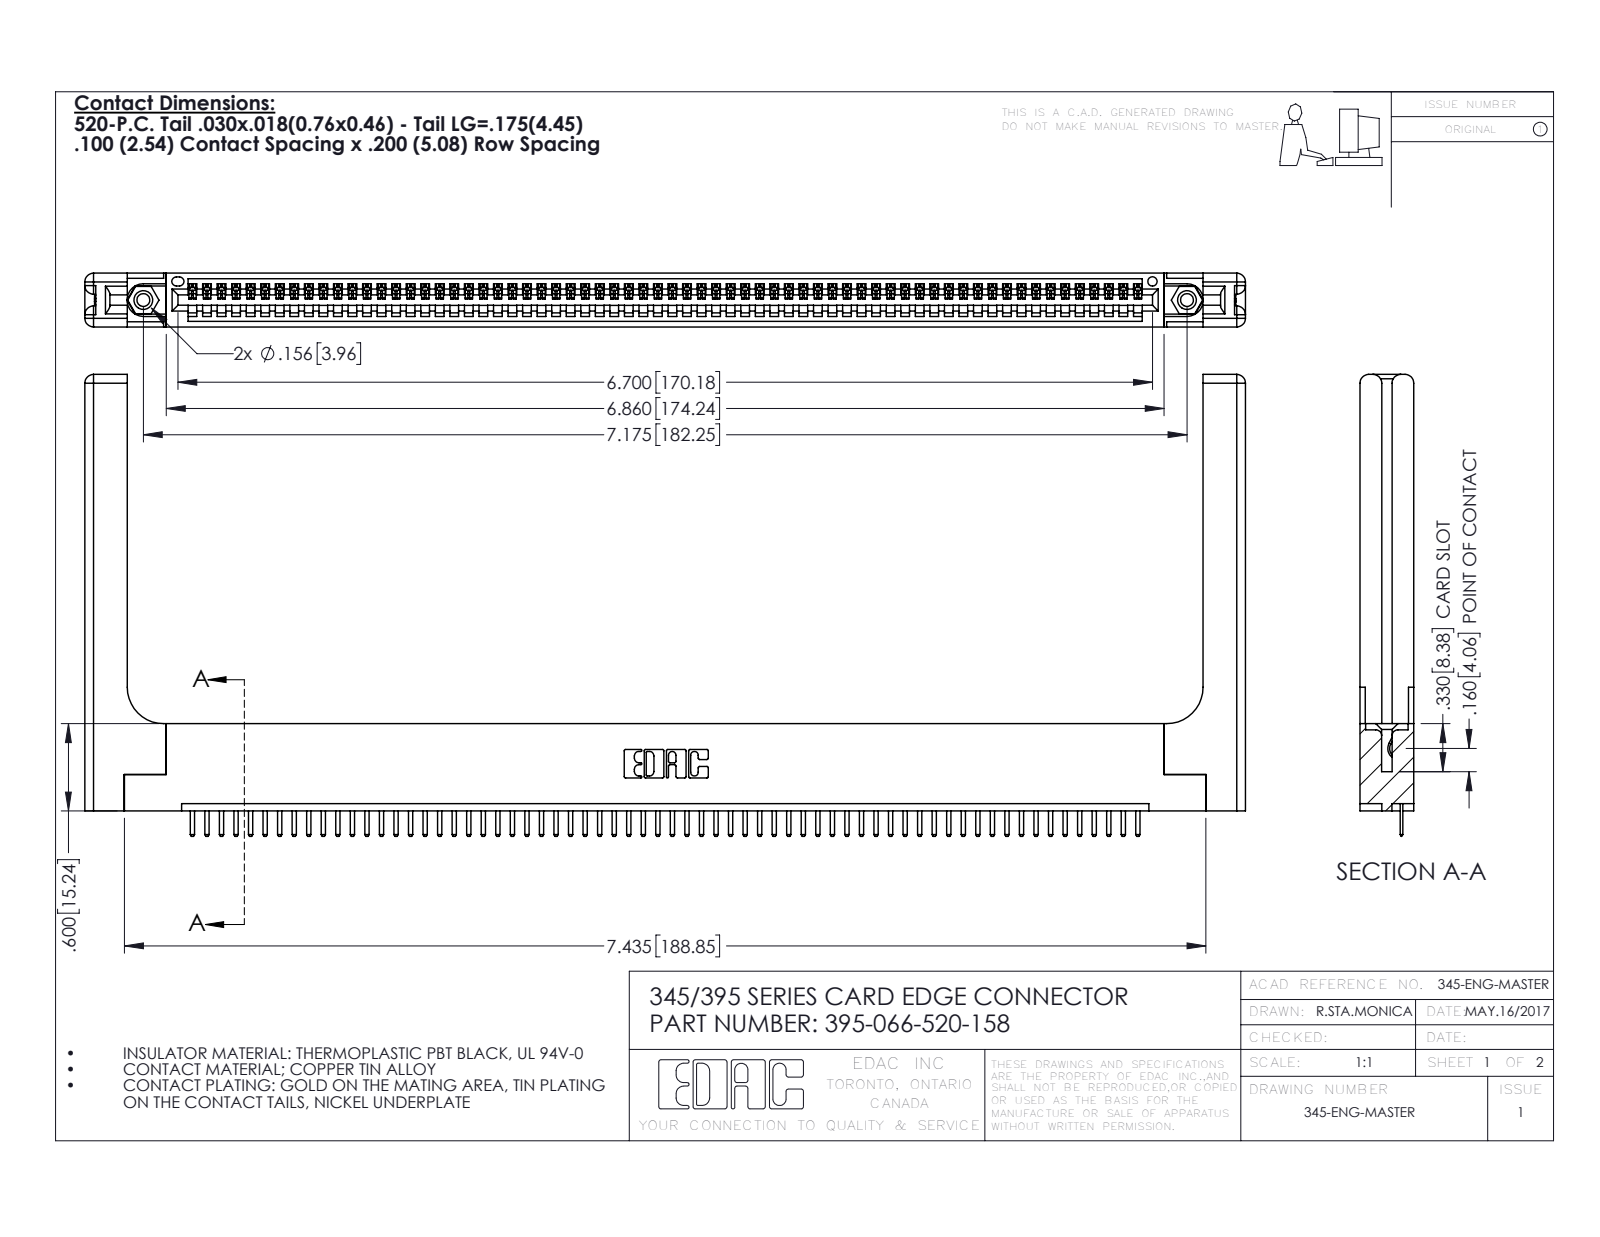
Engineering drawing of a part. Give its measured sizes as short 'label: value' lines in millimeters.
name: 395-066-520-158; 345-292-001_345-293-120; 345-220-058_345-220-058; 345 Part_Flush Mounting Lugs - 0.156 Dia-TH (+1 more)
written by: SolidWorks 2016 (CONFIG_CONTROL_DESIGN)
unit: mm
bodies: 71 solids, 4474 faces (3000 planar, 1414 cylindrical, 60 other)
size: 202.7 × 80.6 × 9.4
volume: 27 760 mm³; area: 30 600 mm²
holes: 2× ⌀2.3, 2× ⌀3.2, 2× ⌀4, 1× ⌀1.6
bosses: 2× ⌀3.9
rounds: 134× R0.3, 132× R0.2, 22× R0.3, 16× R1.5, 6× R0.2, 6× R0.8, 3× R0.7, 2× R0.8
face distances: 1.8, 9.4, 7.6, 5.1, 2.5, 6.9, 0.6, 5.7, 3.8, 3.8
hole spacings: 6.9, 176.3, 182.2
